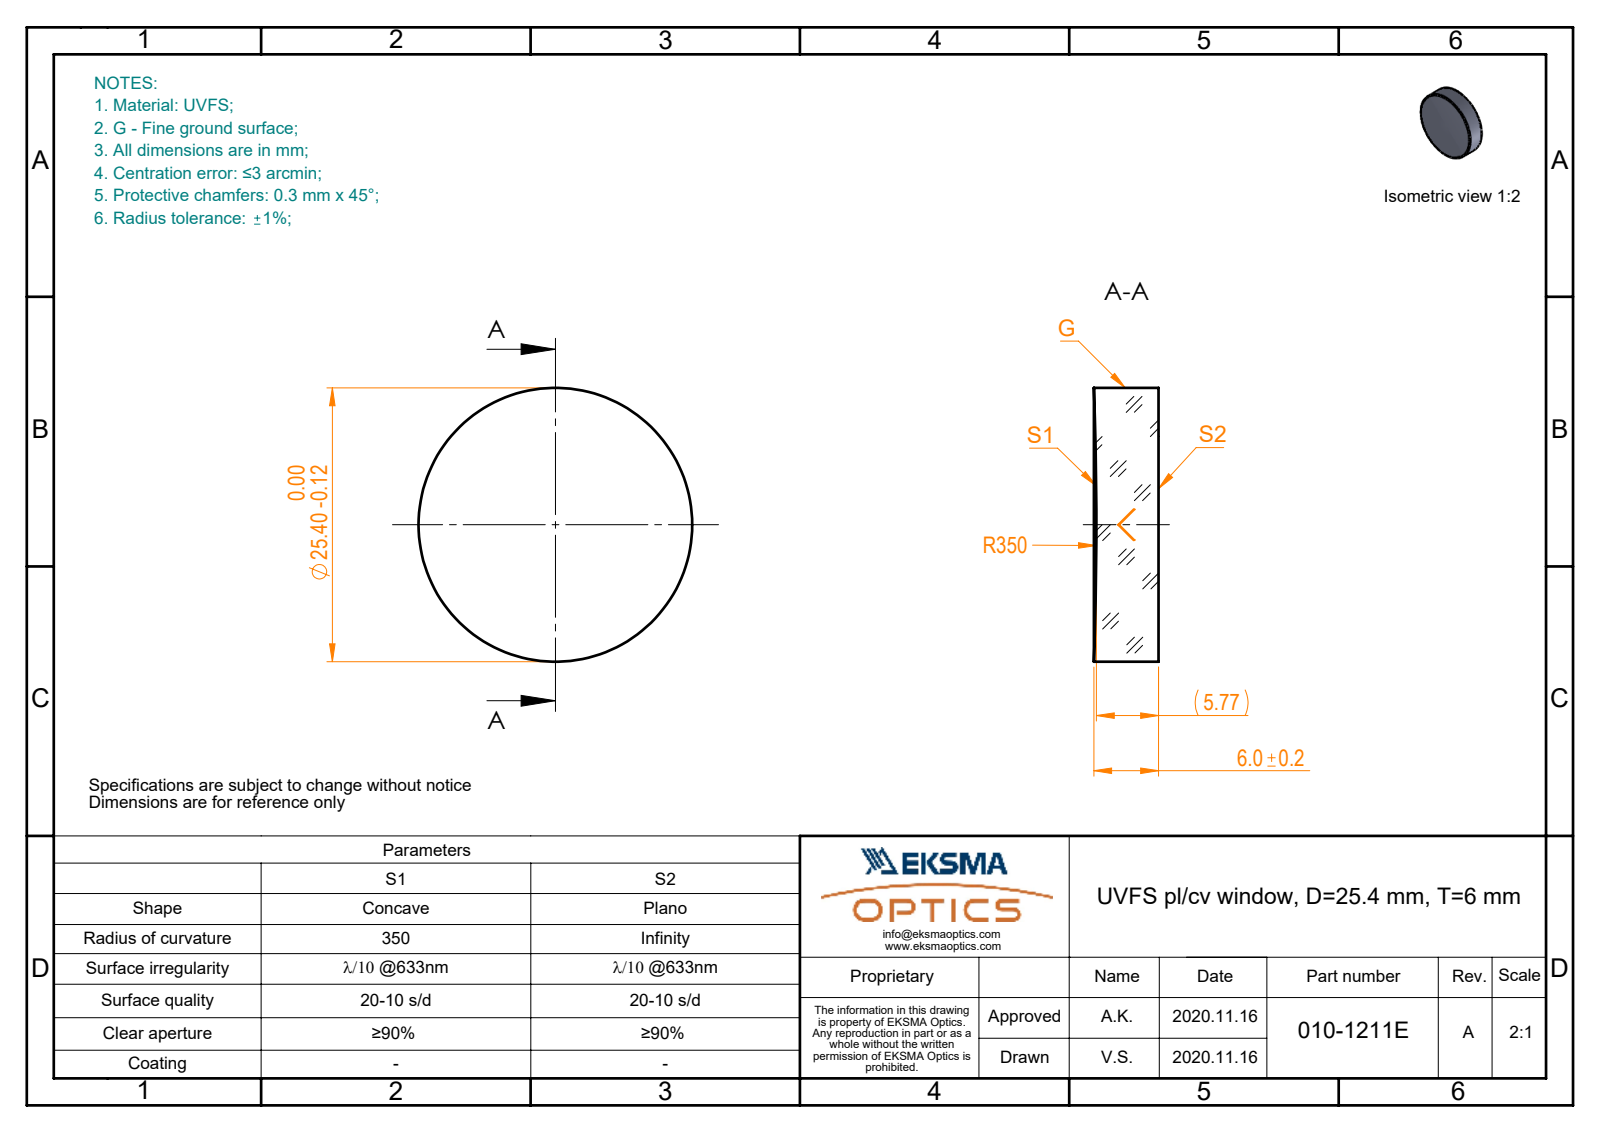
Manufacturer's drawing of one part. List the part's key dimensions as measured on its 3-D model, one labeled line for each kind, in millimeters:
Part name (STEP PRODUCT): 010-1211E_UVFS_PCV_window
STEP written by: SolidWorks 2019 (CONFIG_CONTROL_DESIGN)
Units: millimetres
Bodies: 1 solid, 5 faces (1 planar, 2 cylindrical, 2 other)
Overall size (bounding box): 25.4 × 25.4 × 6
Volume: 2 982 mm³ · Surface area: 1 492 mm²
Round bosses / shafts (diameter × count): ⌀25.4 ×1
